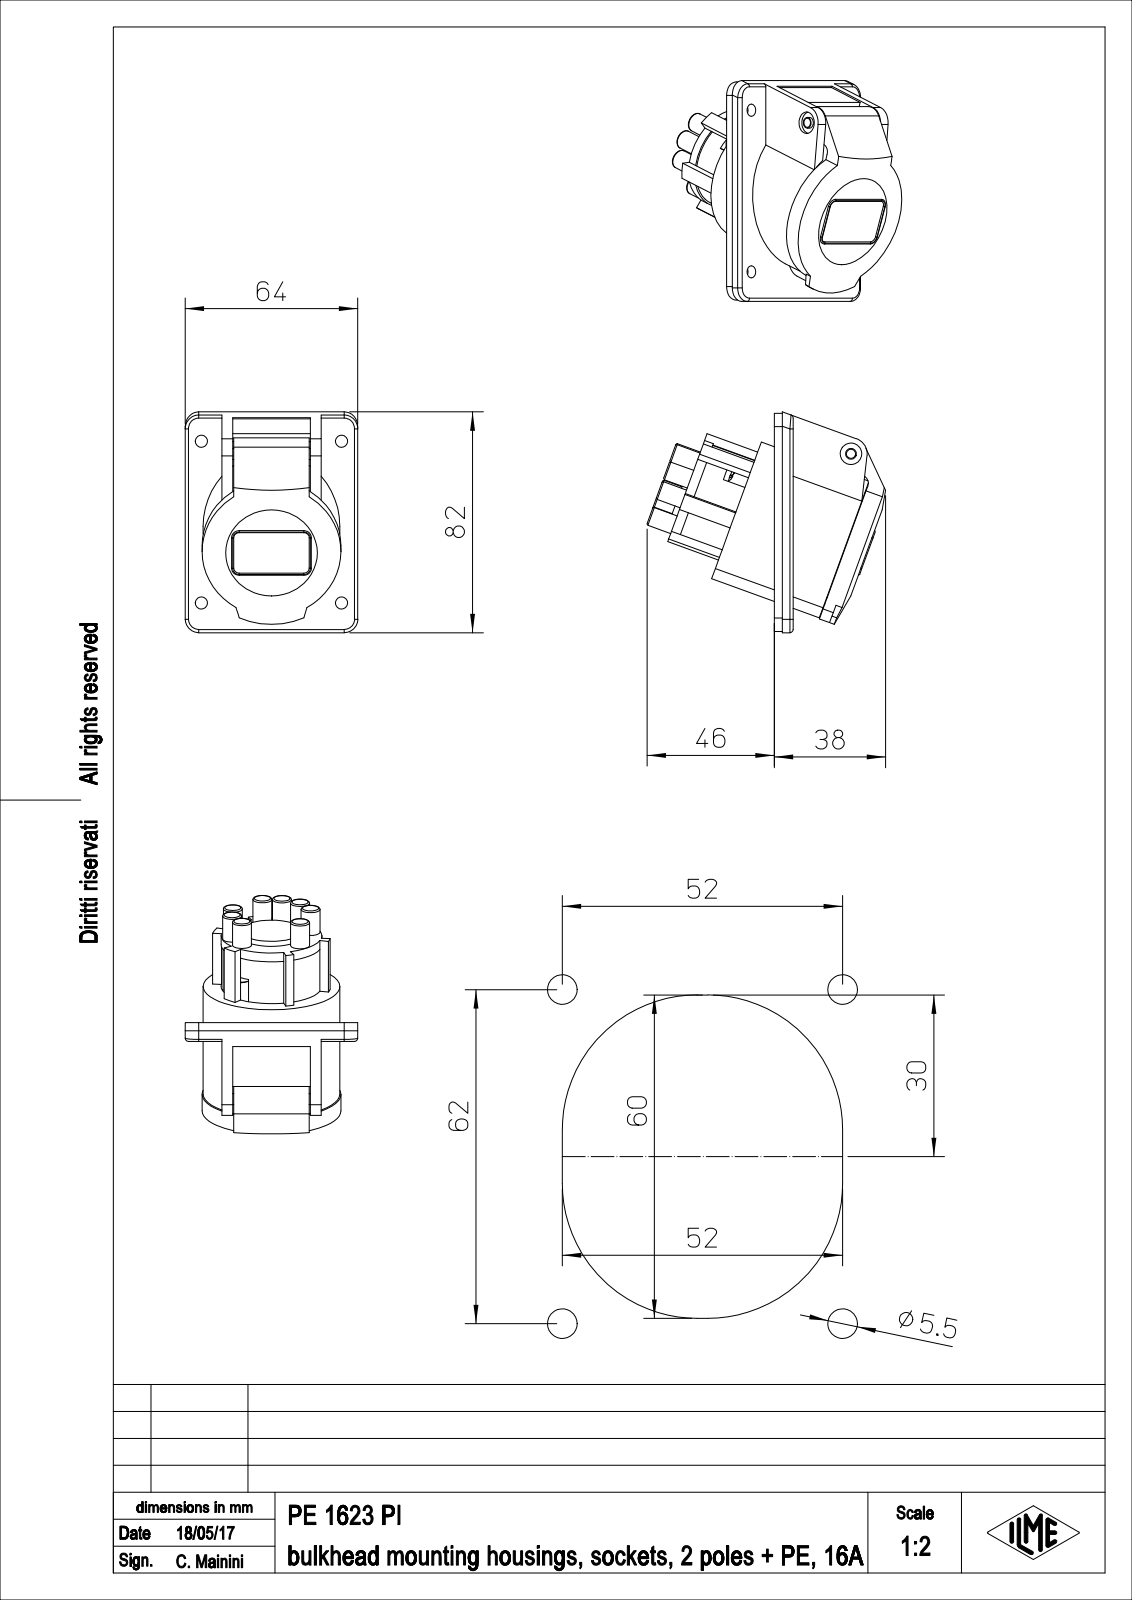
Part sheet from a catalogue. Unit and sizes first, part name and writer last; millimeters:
Units: millimetres
Overall size (bounding box): 80.6 × 77.61 × 64
Round holes (diameter × count): ⌀4.5 ×4, ⌀5.5 ×4, ⌀3.4 ×1, ⌀8 ×1, ⌀37.5 ×1, ⌀44.7 ×1
Round bosses / shafts (diameter × count): ⌀7 ×8, ⌀6.4 ×2, ⌀50.7 ×1, ⌀41.5 ×1, ⌀37.4 ×1, ⌀36 ×1, ⌀23 ×1, ⌀4 ×1
Partial cylindrical surfaces — rounded edges, fillets, slot ends (radius × count): R5 ×8, R0.4 ×4, R1.2 ×4, R4 ×2, R6 ×2, R6.5 ×2, R28 ×2, R2.5 ×1
Main face-to-face distances: 6.99, 3, 4, 1.7, 41, 8, 32.8, 42.7, 13.6, 46.4
Hole centre spacings: 52, 79.4, 60, 60.01
Volume: 128 284 mm³ · Surface area: 46 891 mm²
Bodies: 1 solid, 272 faces (120 planar, 114 cylindrical, 38 other)
Part name (STEP PRODUCT): PE_1623_PI
STEP written by: PTC Creo Elements/Direct Modeling 19.0E 27-Jun-2016 (C) Parametric Technology GmbH (AUTOMOTIVE_DESIGN)
